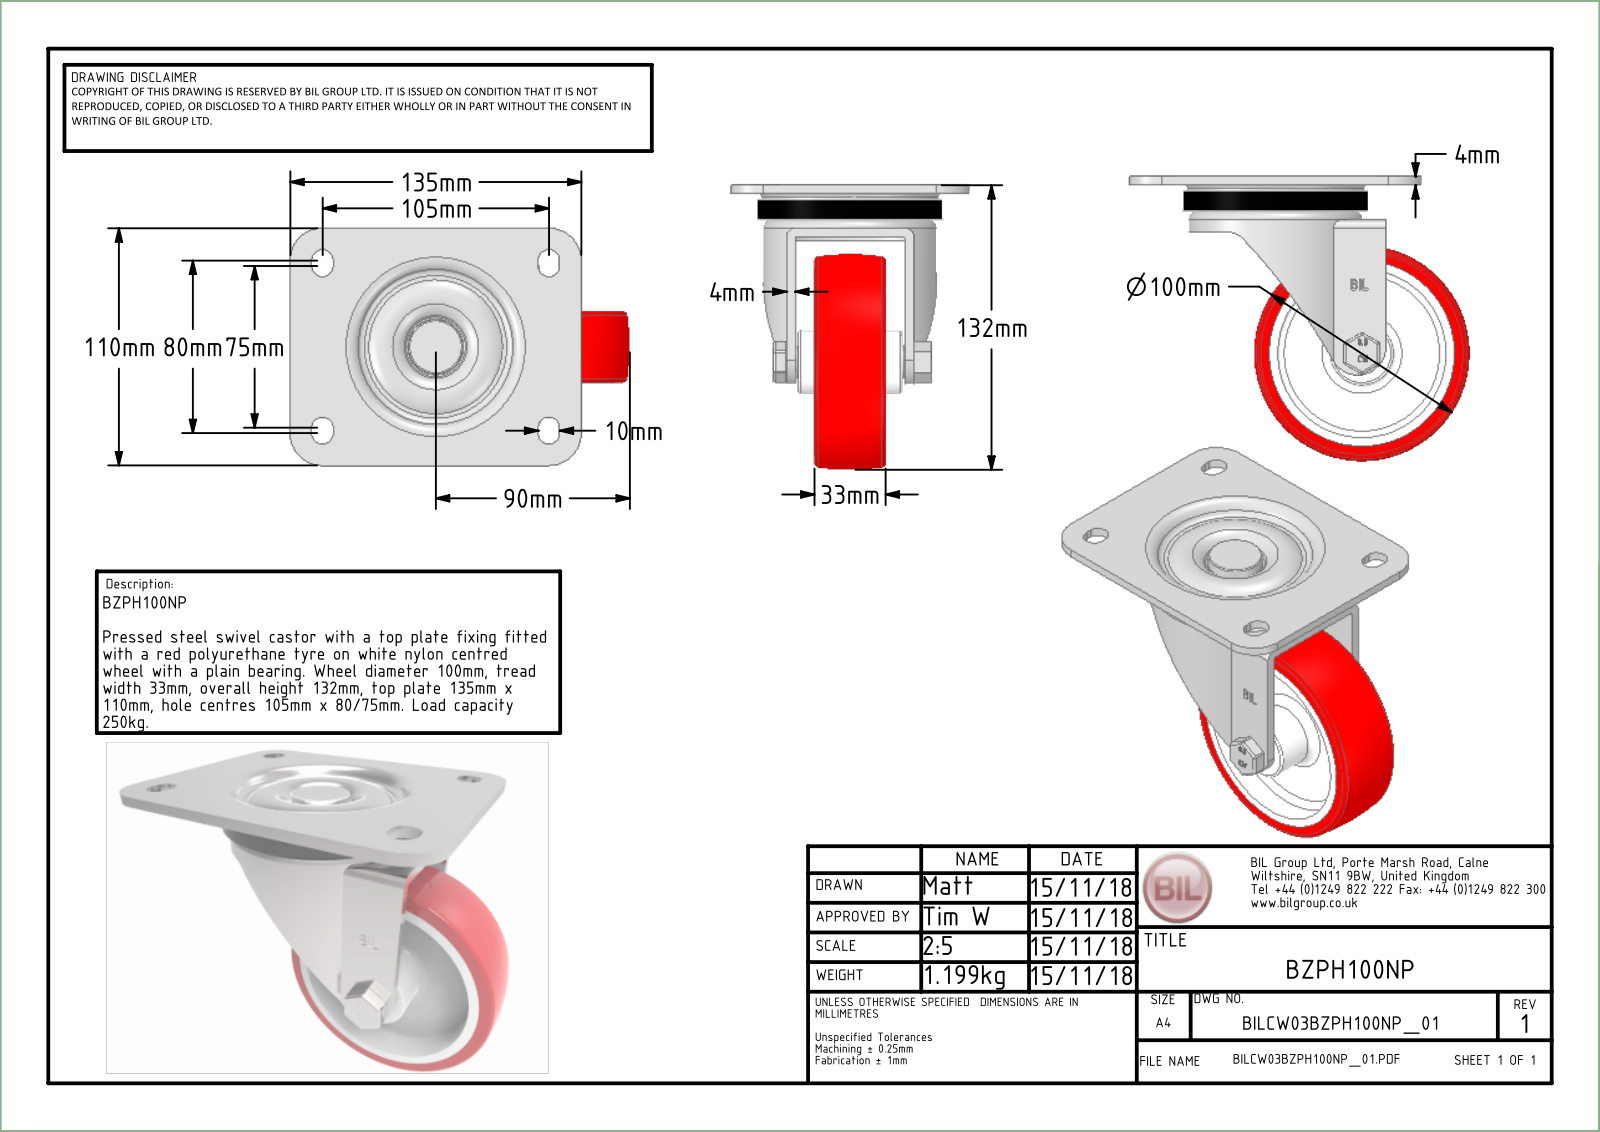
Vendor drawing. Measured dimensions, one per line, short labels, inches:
name: BZPH100NP v3; BZPH100AS v1; ZINC PLATED, PRESSED STEEL TOP PLATE; ZINC PLATED, PRESSED STEEL FORKS (+8 more)
written by: Autodesk Translation Framework v14.10.0.0 (AUTOMOTIVE_DESIGN)
unit: in
bodies: 10 solids, 392 faces (183 planar, 117 cylindrical, 92 other)
size: 6.201 × 5.197 × 4.331
volume: 19.47 in³; area: 212.9 in²
holes: 1× ⌀0.394, 1× ⌀0.402, 1× ⌀0.413, 1× ⌀0.472, 1× ⌀0.606, 1× ⌀1.024, 1× ⌀1.102, 1× ⌀2.835, 1× ⌀3.228, 1× ⌀3.248
bosses: 1× ⌀3.287, 1× ⌀3.15, 1× ⌀2.008, 1× ⌀1.26, 1× ⌀1.181, 1× ⌀0.984, 1× ⌀0.827, 1× ⌀0.63
rounds: 18× R0.02, 8× R0.217, 6× R0.03, 4× R0.079, 4× R0.591, 2× R0.157, 1× R0.535, 1× R0.63
face distances: 0.157, 0.354, 0.512, 0.748, 0.551, 0.197, 1.811, 1.063, 1.26, 2.165
